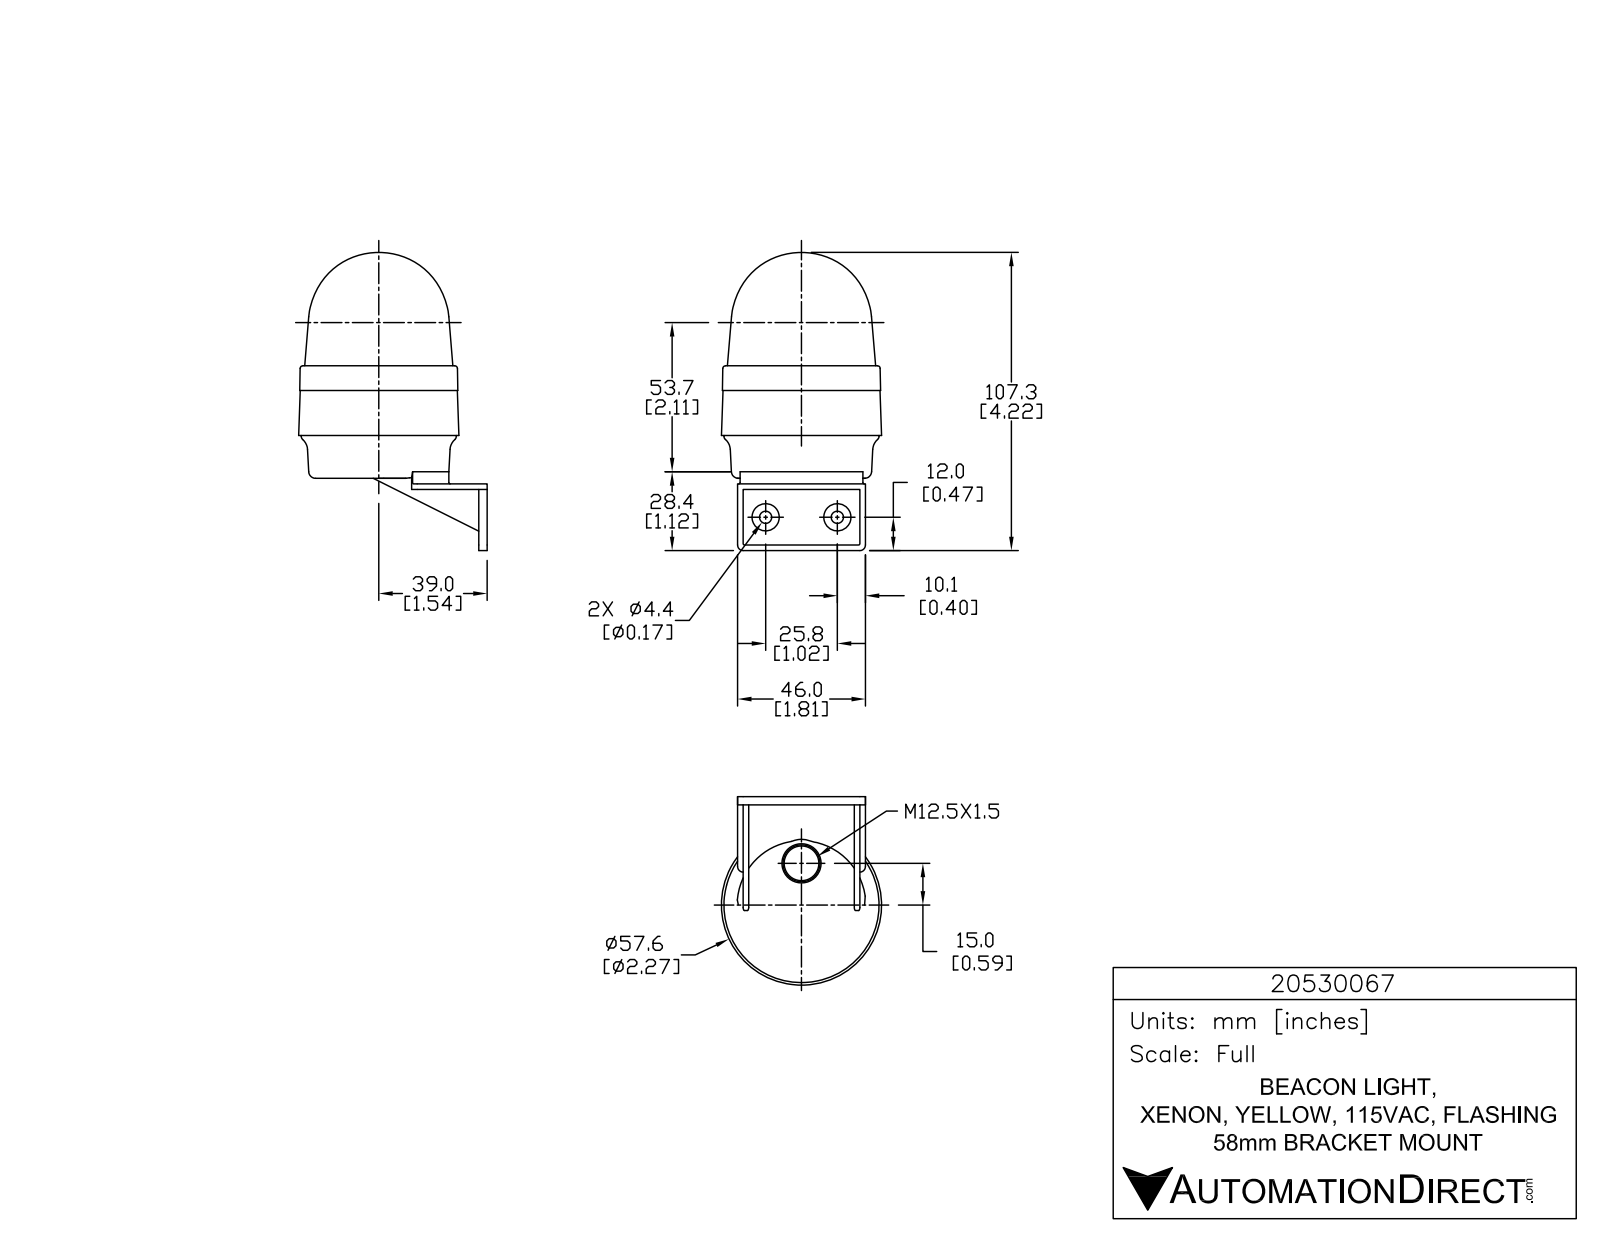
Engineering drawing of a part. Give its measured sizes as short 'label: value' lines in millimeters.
name: 20530067
written by: SolidWorks 2015 (AUTOMOTIVE_DESIGN)
unit: mm
bodies: 1 solid, 828 faces (551 planar, 179 cylindrical, 98 other)
size: 107.3 × 72.4 × 61.1
volume: 168 300 mm³; area: 21 540 mm²
holes: 3× ⌀1, 2× ⌀4.4
bosses: 3× ⌀5.7, 3× ⌀1.4, 2× ⌀9.8, 1× ⌀55.8
rounds: 6× R0.2, 6× R0.2, 6× R0.2, 6× R0.5, 6× R3.3, 4× R2, 3× R0.1, 3× R0.1
face distances: 2, 4, 40, 42, 1, 3, 38, 22, 24, 19.4
hole spacings: 25.8
